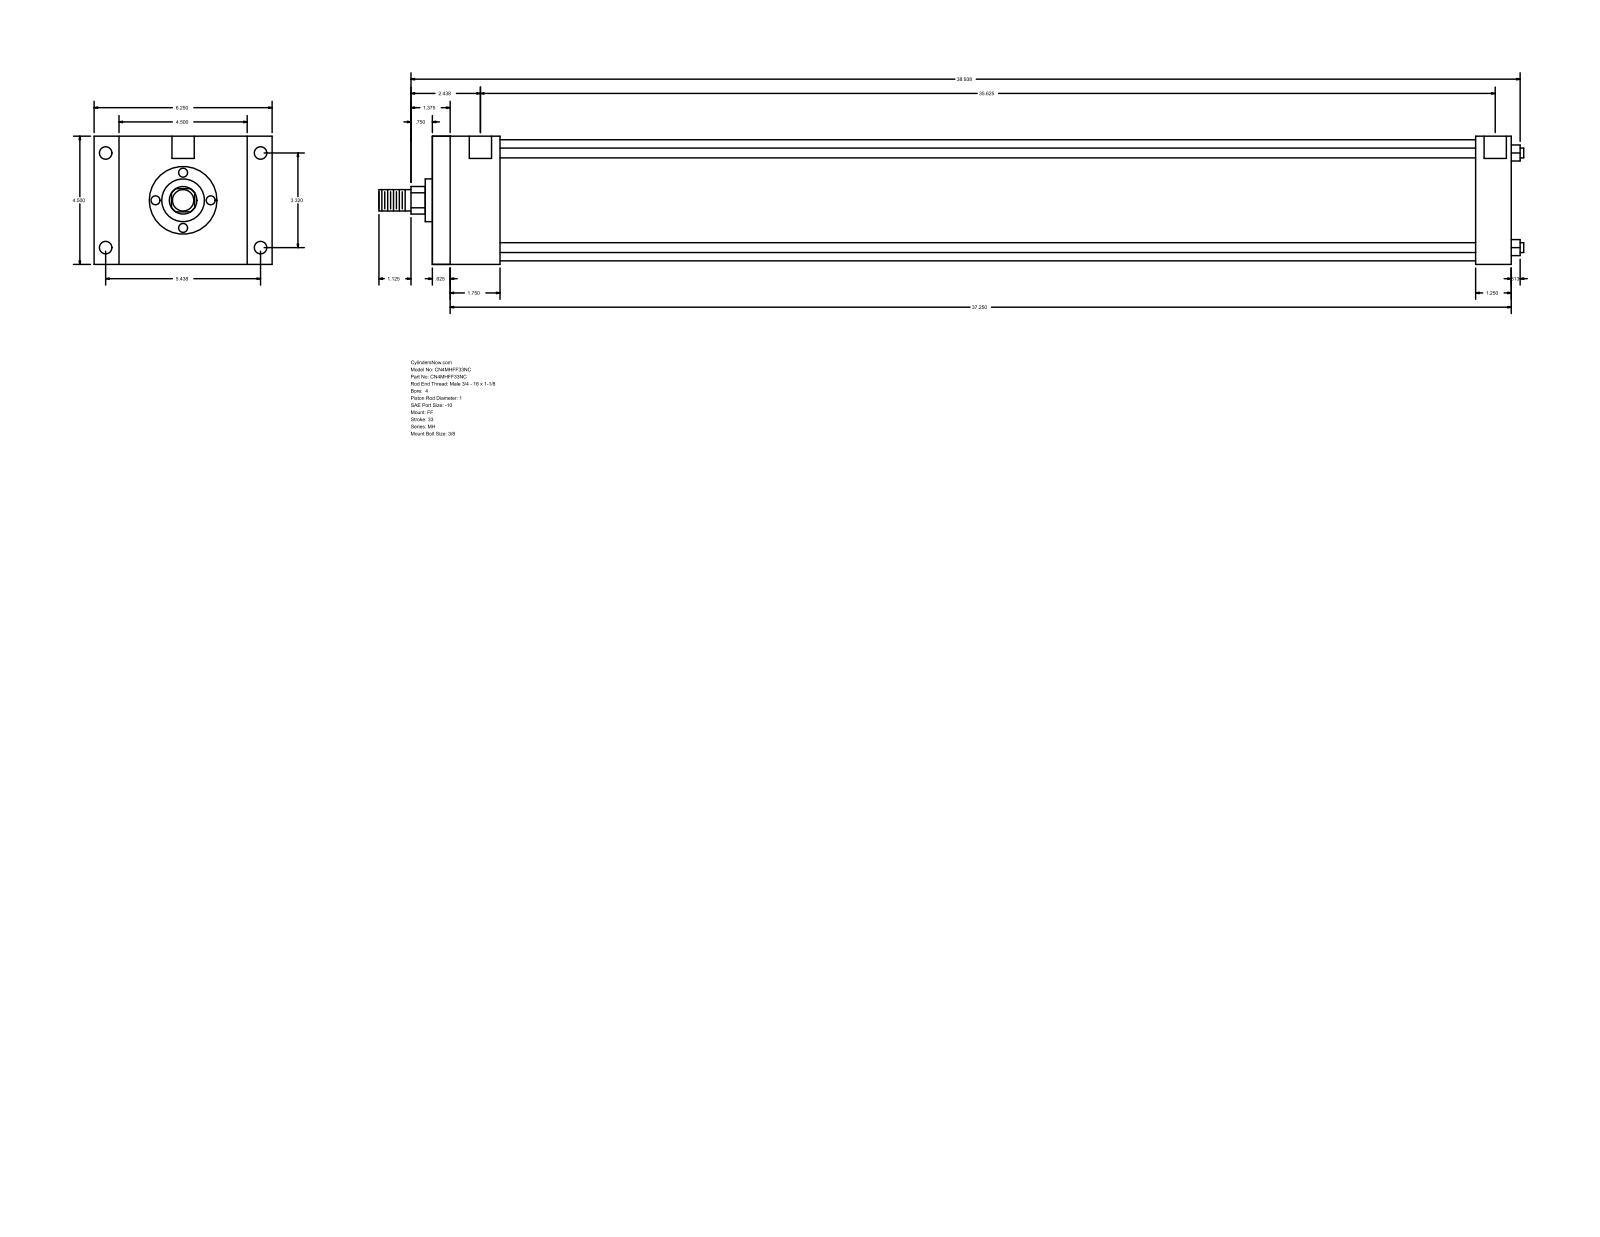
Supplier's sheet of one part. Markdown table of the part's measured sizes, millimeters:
| quantity | value |
| --- | --- |
| part name | MH_FF__0400_1 |
| STEP written by | GSSL Pune (CONFIG_CONTROL_DESIGN) |
| units | millimeters |
| bodies | 0 solids, 92 faces (64 planar, 28 cylindrical, 0 other) |
| overall size | 1020.76 × 158.75 × 114.3 |
| round holes (diameter × count) | 8.73 × 4, 11.13 × 4, 19.84 × 2 |
| round bosses / shafts (diameter × count) | 8.76 × 4, 107.95 × 1, 38.1 × 1, 25.4 × 1, 19.05 × 1 |
| partial cylindrical surfaces (radius × count) | 12.29 × 1 |
| main face-to-face distances | 114.3, 962.03, 15.87, 946.16, 60.33, 44.46, 901.7, 930.28, 914.41, 869.95 |
| hole center spacings | 84.32, 138.12, 161.82, 908.05, 1.58, 1.59, 904.88, 906.46 |
